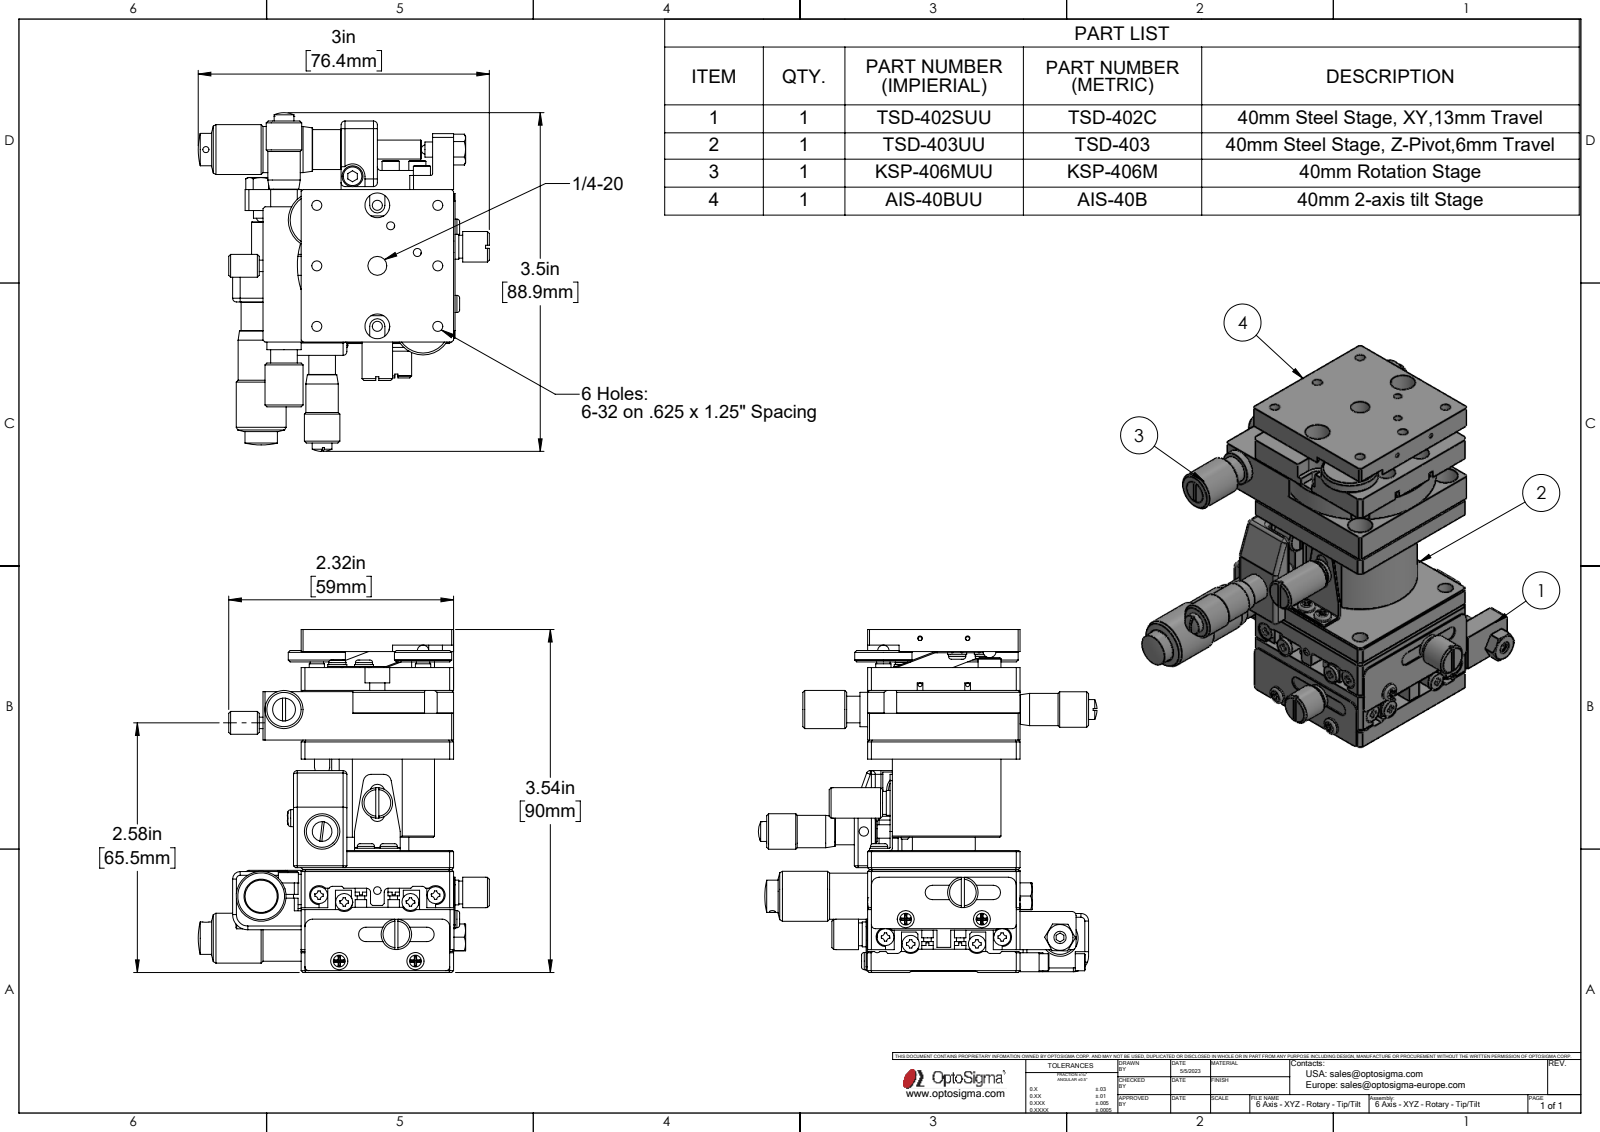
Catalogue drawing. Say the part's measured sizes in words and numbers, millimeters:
The part is named "TSD-403UU-C1C-S07^TSD-403UU(2)_TSD-403UU; KSP-406MUU(2)^KSP-406MUU; AIS-40BUU; TSD-402SUU-C1B-S10.stp (+8 more)". Its 3-D file was written by "SolidWorks 2023 (AUTOMOTIVE_DESIGN)". It is 19 solids with 3601 faces: 1298 planar, 1250 cylindrical and 1053 other. Overall it measures 90 by 88.88 by 76.4 millimeters. Its volume is 65 139 cubic millimeters and its surface area 85 759 square millimeters. Round holes: 37 of diameter 1.8, 22 of diameter 2, 15 of diameter 2.6, 14 of diameter 2.11, 8 of diameter 1.57, 8 of diameter 2.11, 8 of diameter 2.4, 8 of diameter 2.64, 7 of diameter 2.46, 6 of diameter 1.57, 5 of diameter 3, 4 of diameter 2.2. Round bosses or shafts: 29 of diameter 4.5, 25 of diameter 3, 8 of diameter 5, 8 of diameter 3.8, 8 of diameter 2.4, 8 of diameter 2, 8 of diameter 1, 7 of diameter 6. Partial cylindrical surfaces (rounded edges, fillets, slot ends): 56 of radius 1, 32 of radius 0.8, 12 of radius 2, 8 of radius 2.5, 6 of radius 1.9, 5 of radius 0.78, 5 of radius 1.5, 5 of radius 3. The main face-to-face distances are 6, 5, 29, 34, 7, 13, 40, 47, 10, 11. The hole center spacings are 7, 14, 6.51, 8.6, 31.75, 32.59, 33.8, 37.62.
